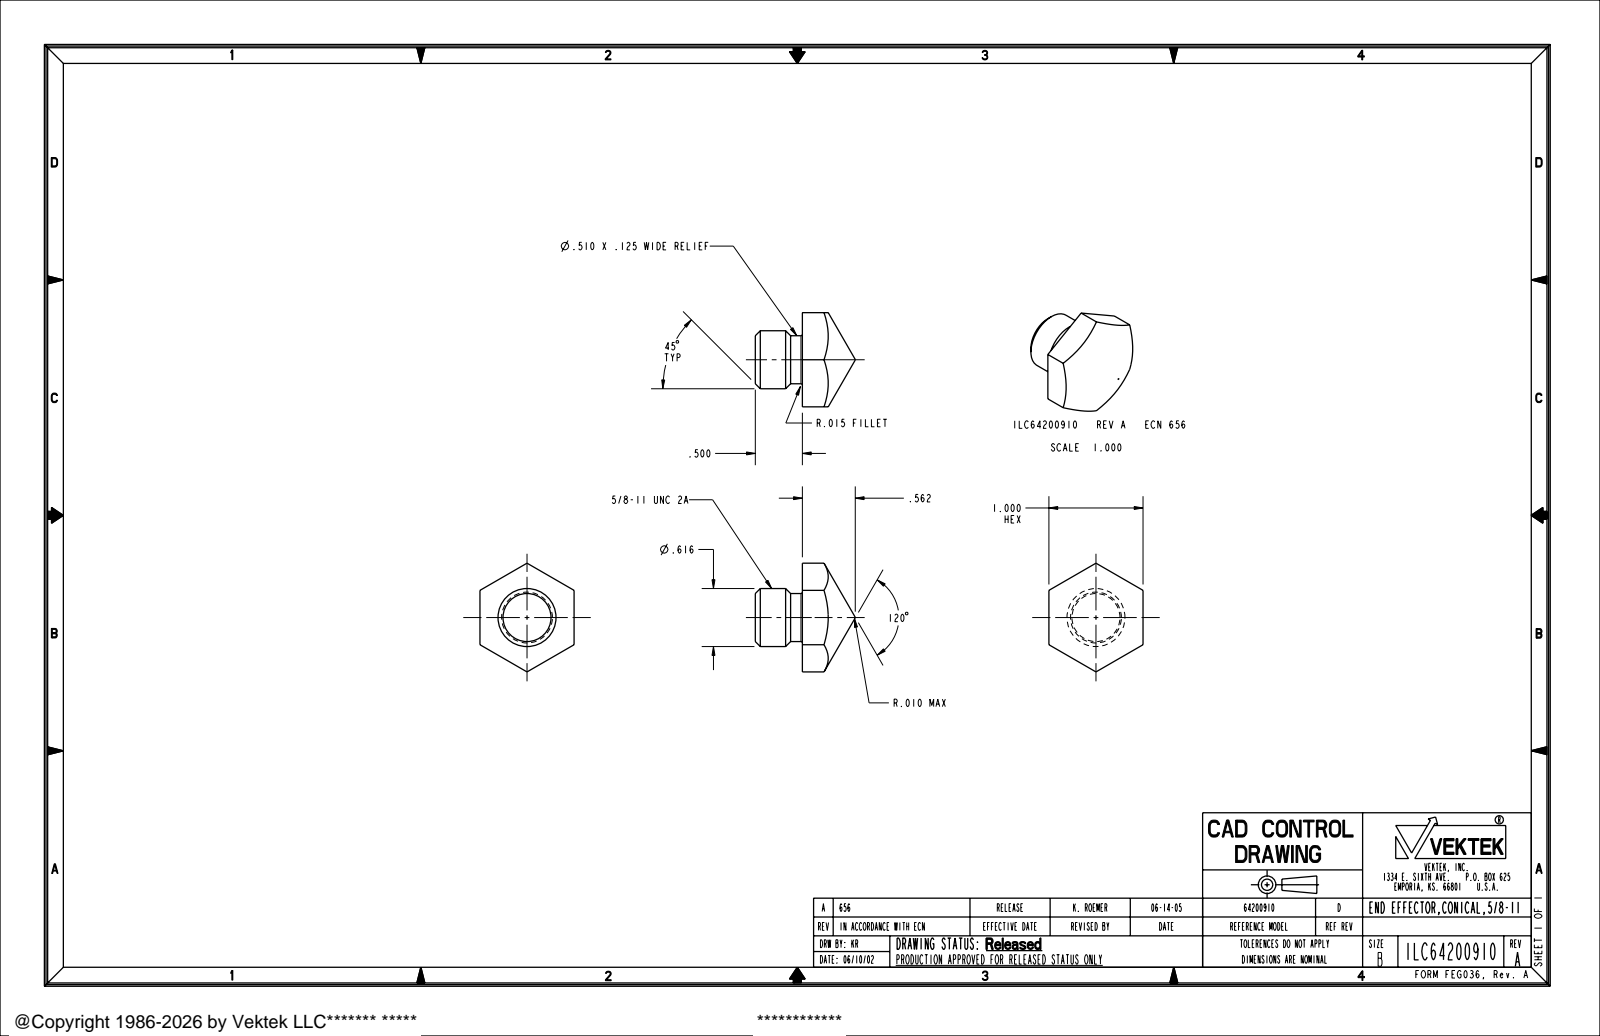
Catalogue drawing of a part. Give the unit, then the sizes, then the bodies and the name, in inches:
Units: inches
Overall size (bounding box): 1.155 × 1.062 × 1
Round bosses / shafts (diameter × count): ⌀0.616 ×1, ⌀0.51 ×1
Main face-to-face distances: 1, 0.5
Volume: 0.445 in³ · Surface area: 3.741 in²
Bodies: 1 solid, 22 faces (8 planar, 4 cylindrical, 10 other)
Part name (STEP PRODUCT): ILC64200910
STEP written by: PRO/ENGINEER BY PARAMETRIC TECHNOLOGY CORPORATION, 2004290 (AUTOMOTIVE_DESIGN_CC2)
